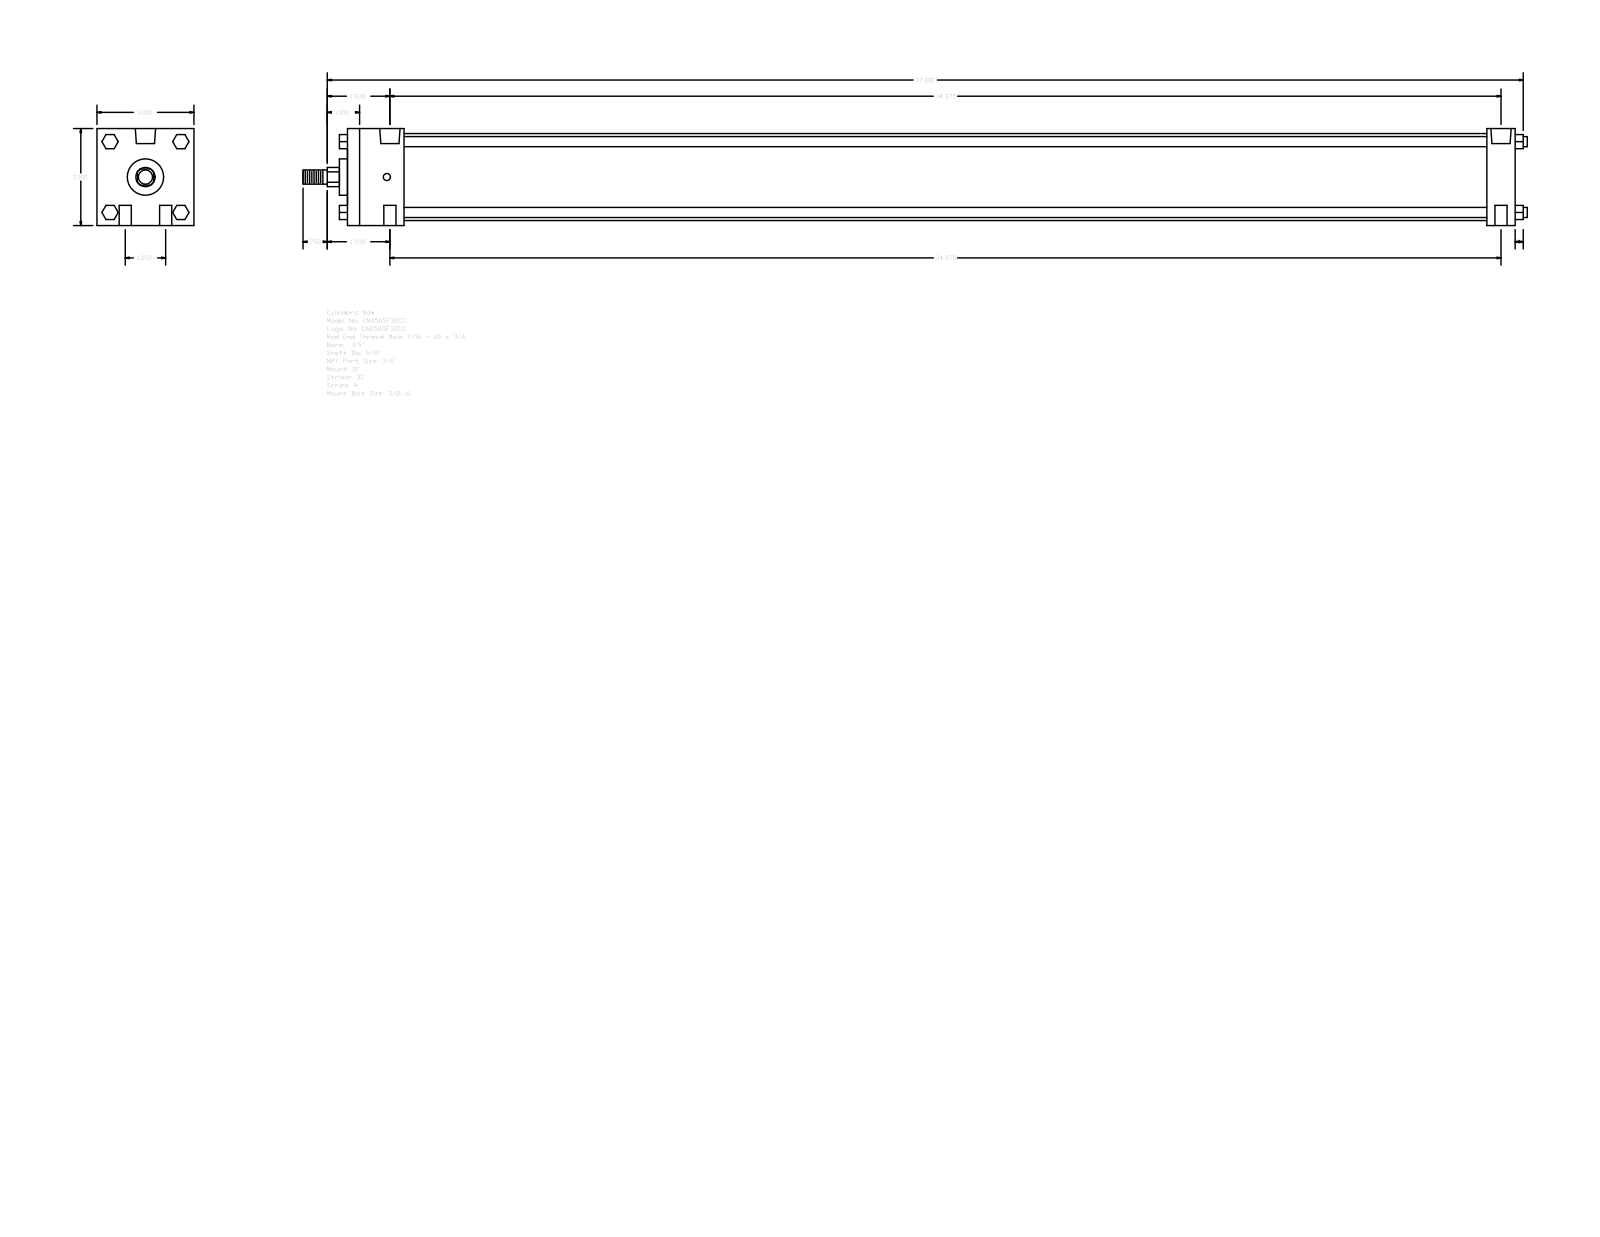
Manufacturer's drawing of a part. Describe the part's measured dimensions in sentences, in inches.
The part is named "A_SF__0250_0.625". Its 3-D file was written by "GSSL Pune (CONFIG_CONTROL_DESIGN)". It is 0 solids with 124 faces: 94 planar, 30 cylindrical and 0 other. Overall it measures 37.875 by 3 by 3 inches. Round holes: 4 of diameter 0.375, 2 of diameter 0.219, 2 of diameter 0.627. Round bosses or shafts: 4 of diameter 0.313, 1 of diameter 2.69, 1 of diameter 1.125, 1 of diameter 0.625, 1 of diameter 0.437. Partial cylindrical surfaces (rounded edges, fillets, slot ends): 1 of radius 0.297. The main face-to-face distances are 3, 36.125, 1.75, 35.25, 0.875, 33.5, 34.375, 0.25, 36.375, 2. The hole center spacings are 0.625, 34.381, 34.375, 1.25, 34.398, 34.563.
